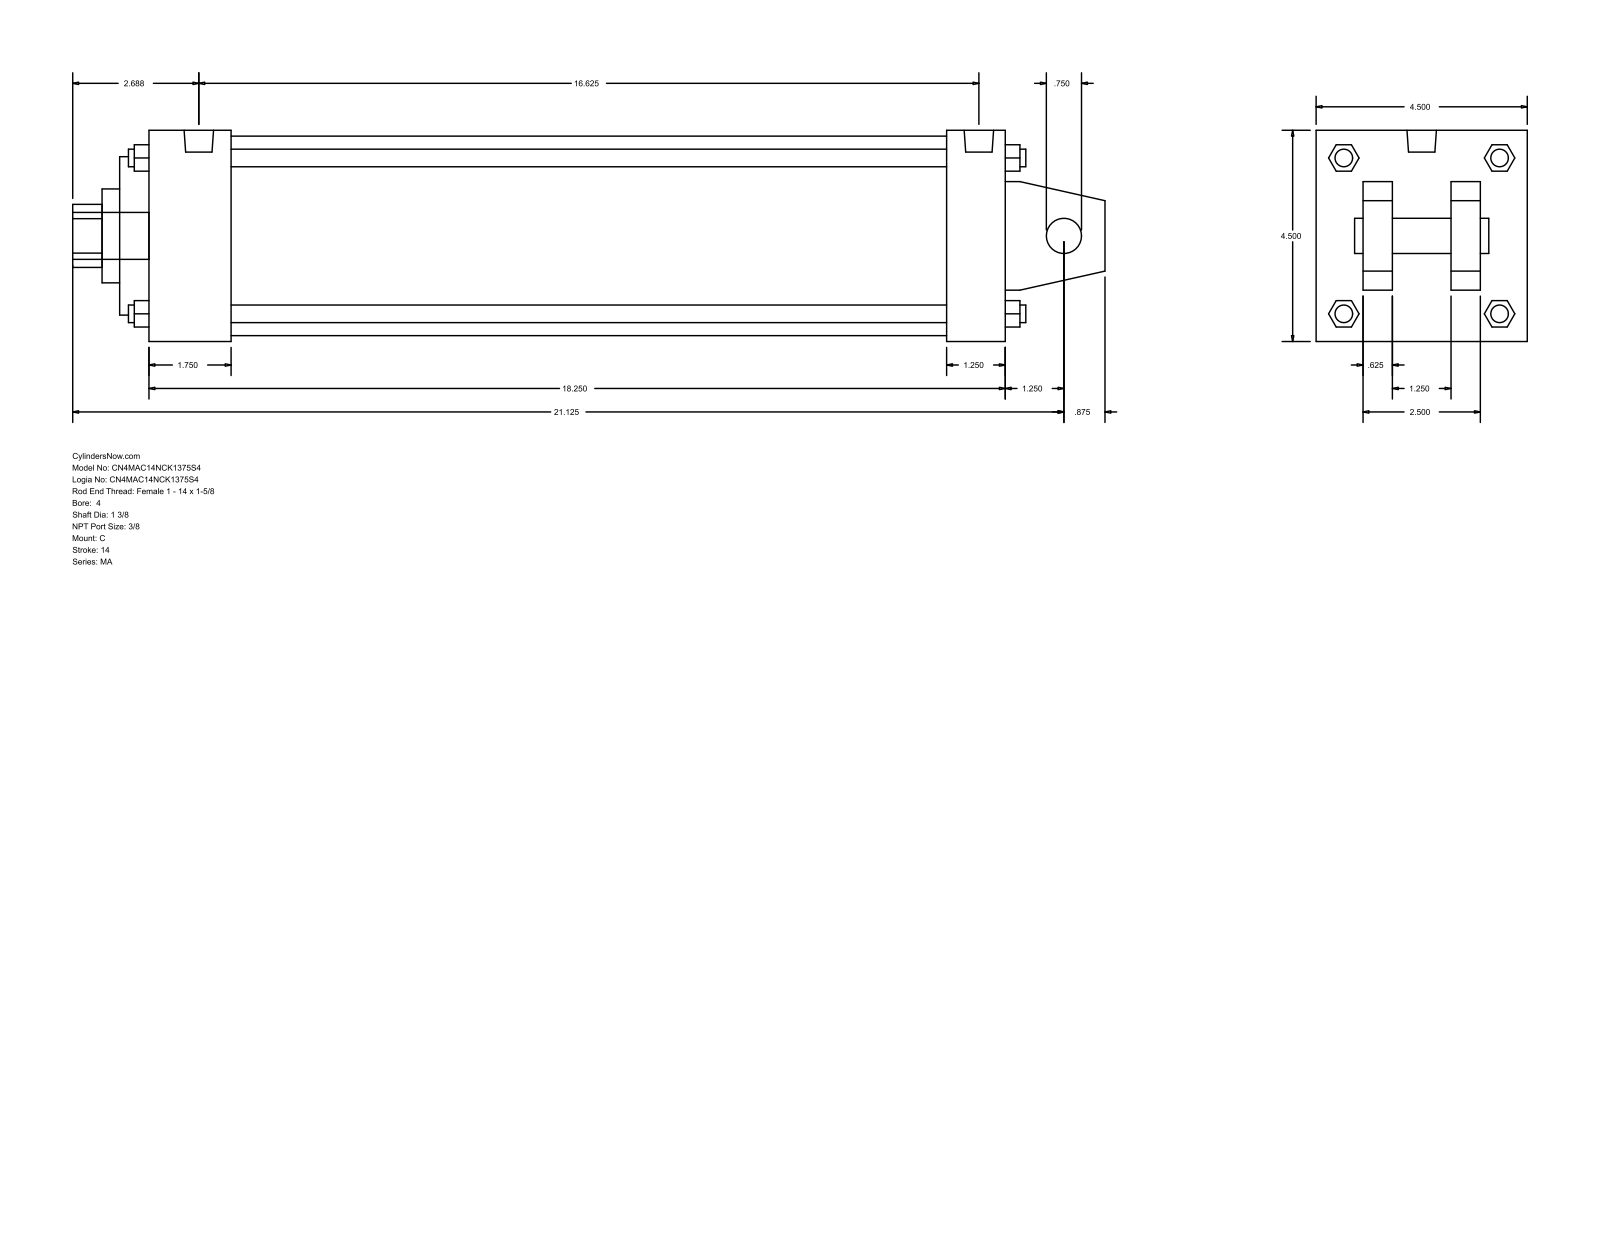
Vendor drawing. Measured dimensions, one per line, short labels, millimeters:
name: MA_C__0400_1.375
written by: GSSL Pune (CONFIG_CONTROL_DESIGN)
unit: mm
bodies: 0 solids, 141 faces (109 planar, 32 cylindrical, 0 other)
size: 558.8 × 114.3 × 114.3
holes: 1× ⌀19.05, 1× ⌀34.92, 1× ⌀50.8, 1× ⌀85.72, 1× ⌀107.95
bosses: 4× ⌀11.11, 4× ⌀9.53, 2× ⌀15.93, 1× ⌀25.4
rounds: 1× R17.06
face distances: 114.3, 15.87, 463.55, 73.03, 41.27, 25.4, 88.9, 47.63, 479.42, 447.67
